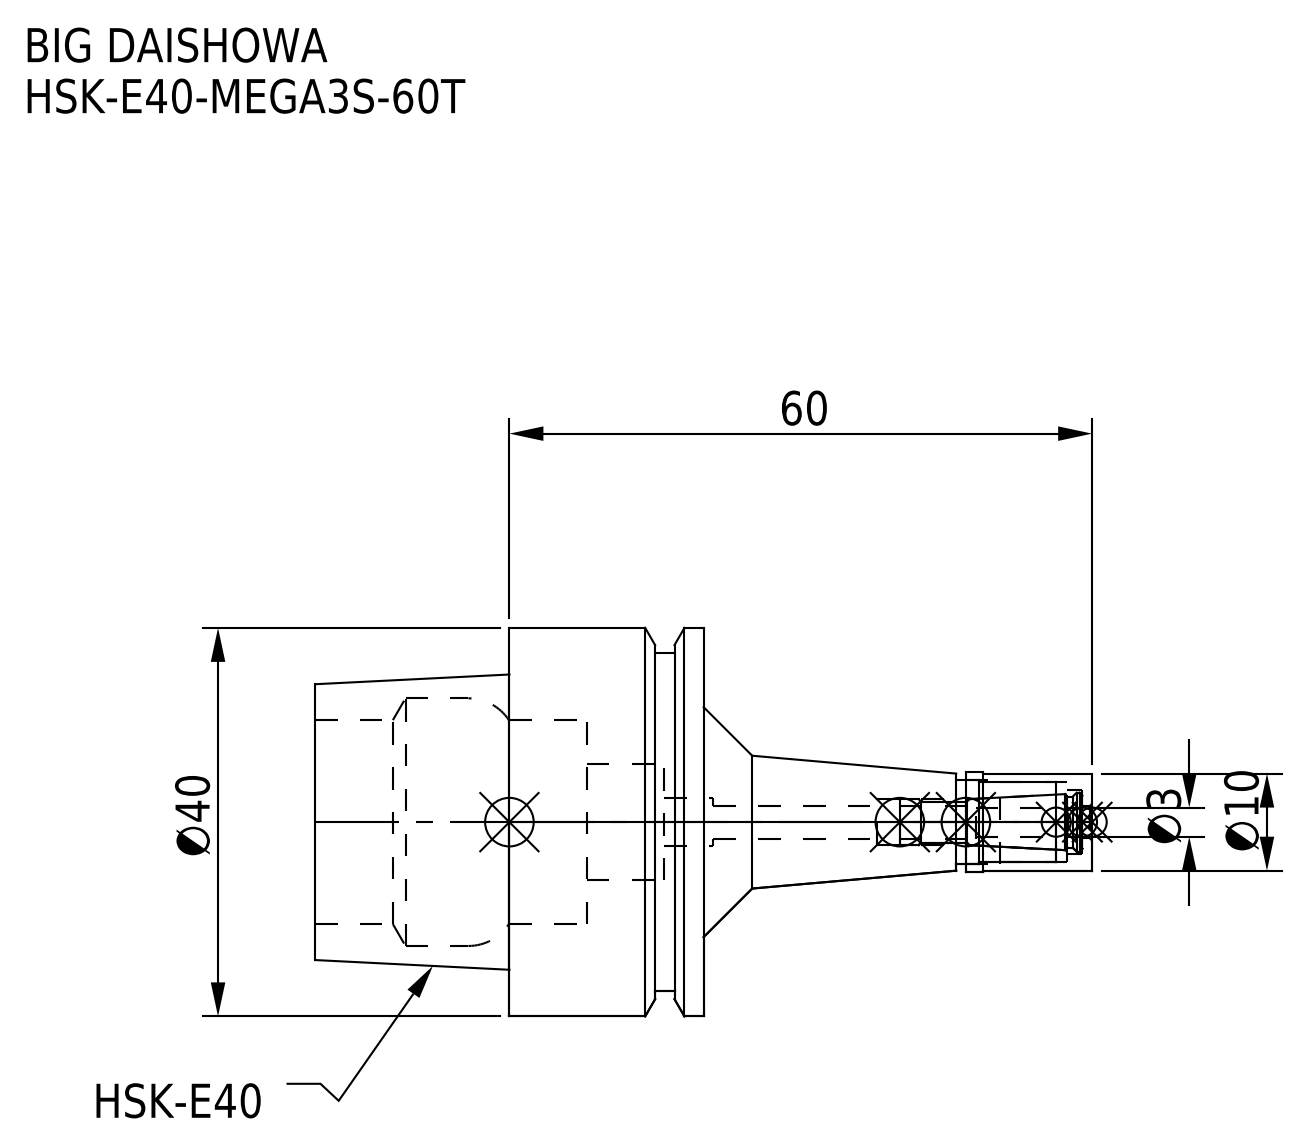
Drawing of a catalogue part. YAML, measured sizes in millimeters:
part_name: "HSK-E40-MEGA3S-60T_1.stp; DXF_TEMP_ASSY_ASM_4_ASM.stp; HSK-E40-MEGA3S-60T-030-FreeParts; HE40MS03060T-030_ASM.stp (+3 more)"
step_written_by: "SolidWorks 2019 (CONFIG_CONTROL_DESIGN)"
units: millimeters
bodies: {solids: 2, faces: 74, planar: 18, cylindrical: 38, other: 18}
overall_size: [80, 40, 40]
volume: 29734
surface_area: 12110
round_holes:
  - {diameter: 3.3, count: 1}
  - {diameter: 3.4, count: 1}
  - {diameter: 4.7, count: 1}
  - {diameter: 5, count: 1}
  - {diameter: 6.6, count: 1}
  - {diameter: 8.2, count: 1}
  - {diameter: 8.7, count: 1}
  - {diameter: 12, count: 1}
  - {diameter: 21, count: 1}
  - {diameter: 25.5, count: 1}
round_bosses_or_shafts:
  - {diameter: 40, count: 1}
  - {diameter: 34.8, count: 1}
  - {diameter: 10.3, count: 1}
  - {diameter: 10, count: 1}
face_to_face_distances: [20, 40, 12.05, 7.95, 27.95, 8, 4.05, 15.95, 35.95, 5]
